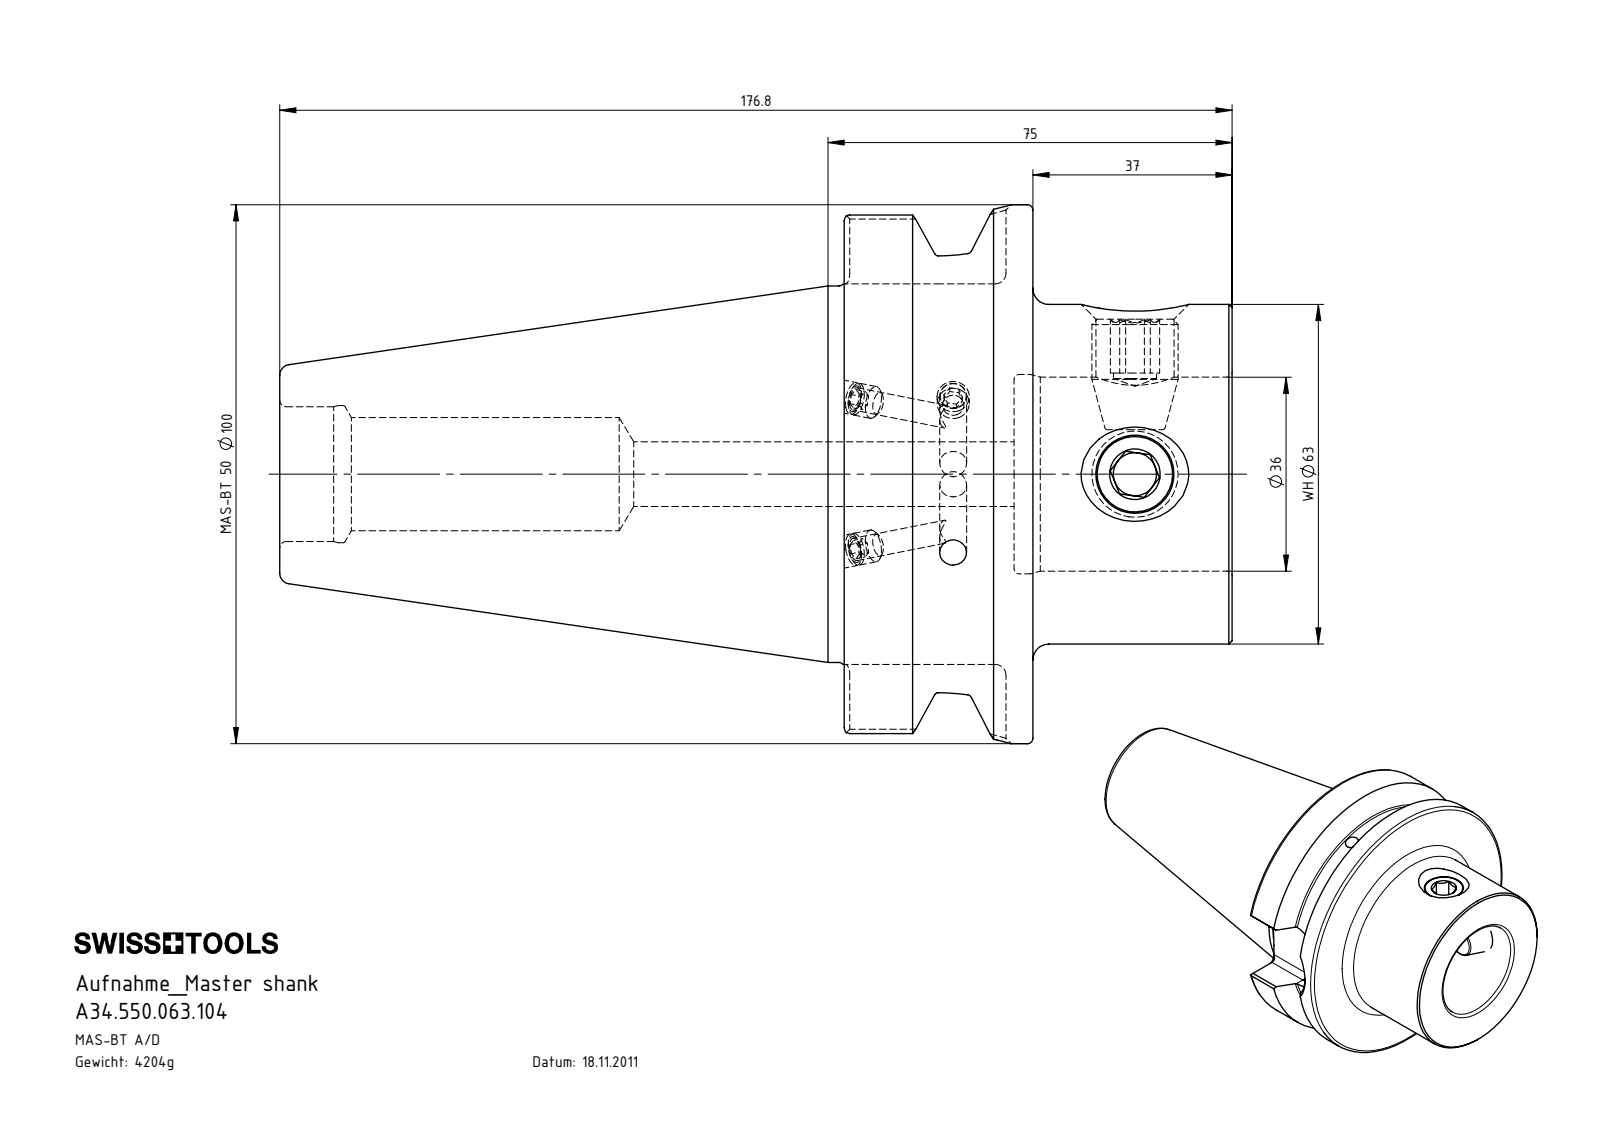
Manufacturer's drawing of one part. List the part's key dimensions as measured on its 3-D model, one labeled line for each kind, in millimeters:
Part name (STEP PRODUCT): WH6-ER1.001.021; BB5-WH6.K01.104_B; ISO 4026 - M6 x 5_PreviewCfg; A34.550.063.104
STEP written by: SolidWorks 2017 (CONFIG_CONTROL_DESIGN)
Units: millimetres
Bodies: 6 solids, 225 faces (75 planar, 63 cylindrical, 87 other)
Overall size (bounding box): 205.8 × 100 × 100
Volume: 622 960 mm³ · Surface area: 75 091 mm²
Round holes (diameter × count): ⌀4.2 ×2, ⌀6 ×2, ⌀8 ×2, ⌀14.5 ×2, ⌀5 ×1, ⌀12 ×1, ⌀21 ×1, ⌀25 ×1, ⌀25.45 ×1, ⌀36 ×1, ⌀37 ×1
Round bosses / shafts (diameter × count): ⌀16 ×2, ⌀100 ×1, ⌀85 ×1, ⌀69.85 ×1, ⌀63 ×1, ⌀6 ×1
Partial cylindrical surfaces — rounded edges, fillets, slot ends (radius × count): R2 ×8, R12.85 ×1
Main face-to-face distances: 35, 101, 66, 60.5, 25.5, 40.5, 70.6, 104.8, 139.8, 165.3
